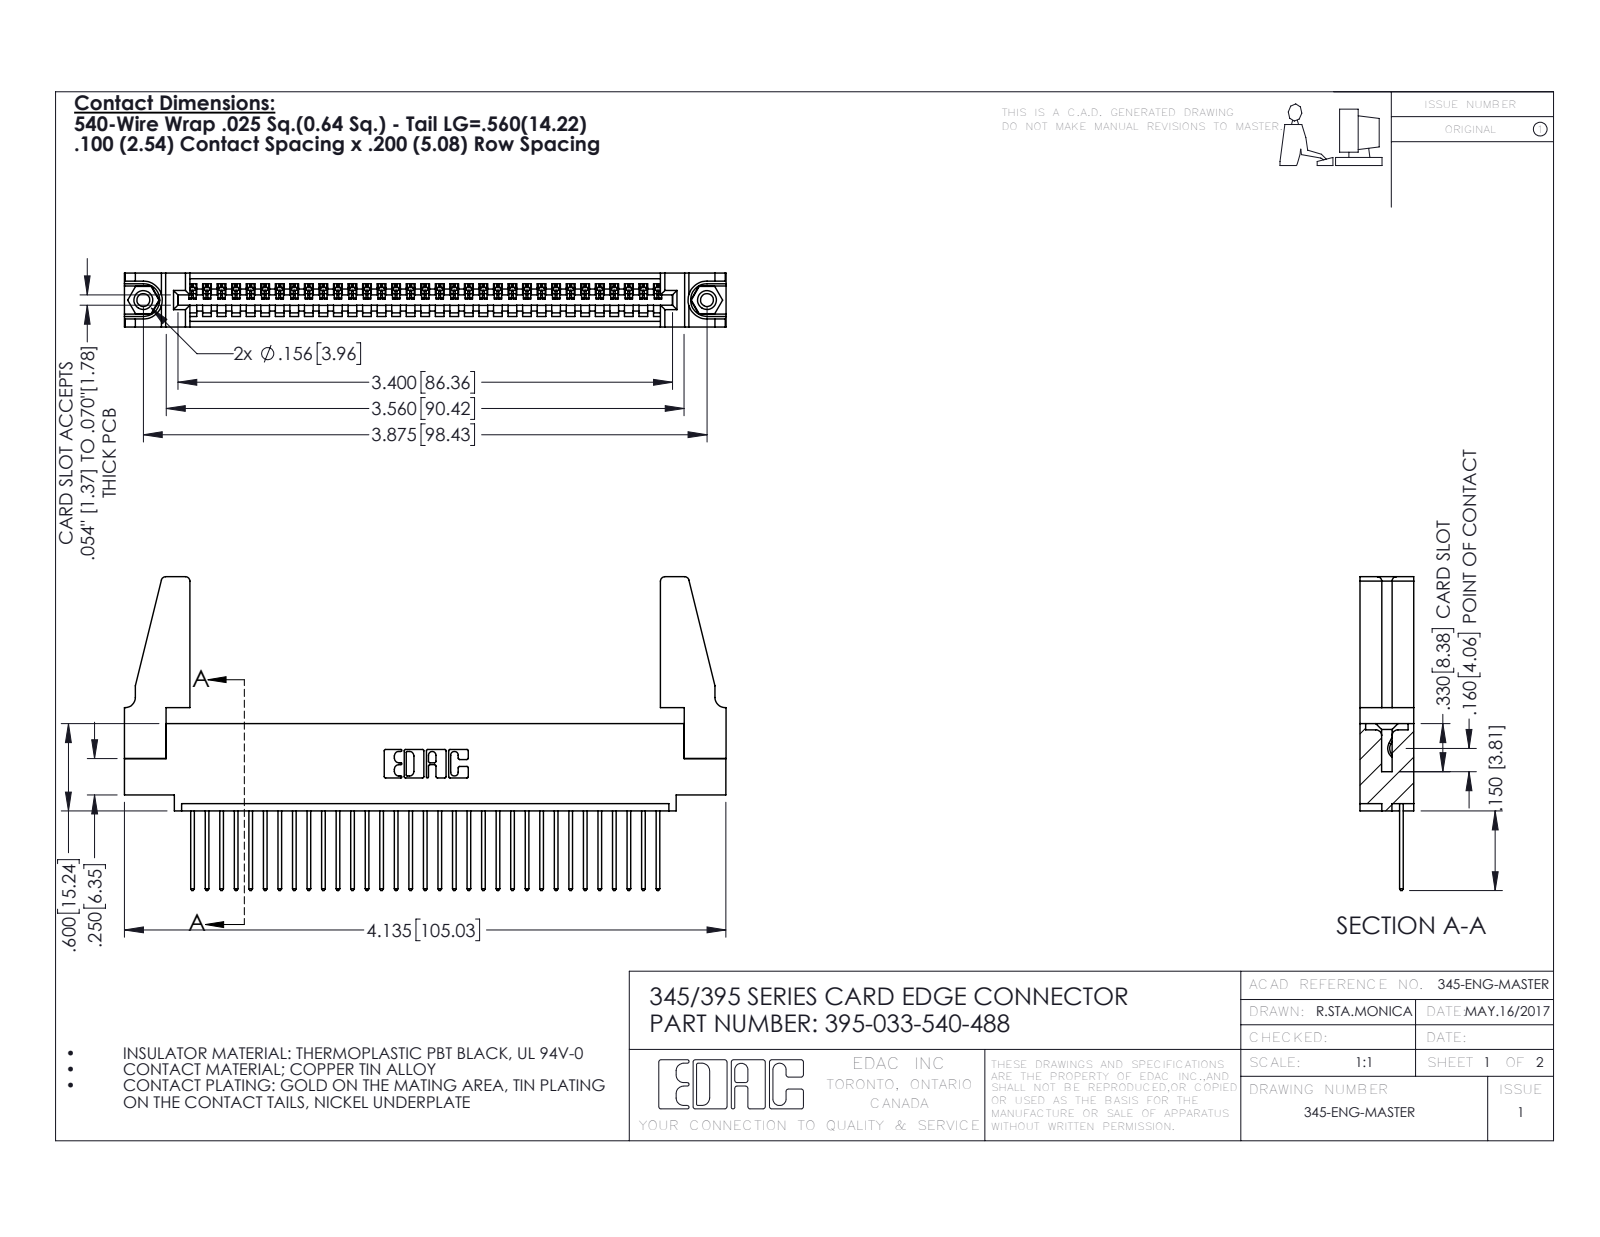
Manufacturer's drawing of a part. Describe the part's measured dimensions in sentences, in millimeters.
The part is named "345-292-001_345-293-140; 395-033-540-488; 345 Part_0.110 Offset - 0.156 Dia-TH; 345-250-001_345-250-001-102 (+1 more)". Its 3-D file was written by "SolidWorks 2016 (CONFIG_CONTROL_DESIGN)". It is 38 solids with 2168 faces: 1476 planar, 676 cylindrical and 16 other. Overall it measures 105.1 by 54.8 by 9.4 millimeters. Its volume is 13 100 cubic millimeters and its surface area 16 540 square millimeters. Round holes: 2 of diameter 2.3, 2 of diameter 3.2, 2 of diameter 4, 1 of diameter 1.6. Round bosses or shafts: 2 of diameter 3.9. Partial cylindrical surfaces (rounded edges, fillets, slot ends): 66 of radius 0.2, 66 of radius 0.3, 22 of radius 0.3, 8 of radius 0.8, 6 of radius 0.2, 6 of radius 0.8, 3 of radius 0.7, 2 of radius 0.8. The main face-to-face distances are 1.8, 7.6, 9.4, 2.5, 6.9, 0.6, 5.1, 5.7, 3.8, 1.8. The hole center spacings are 6.9, 92.5, 98.4.
